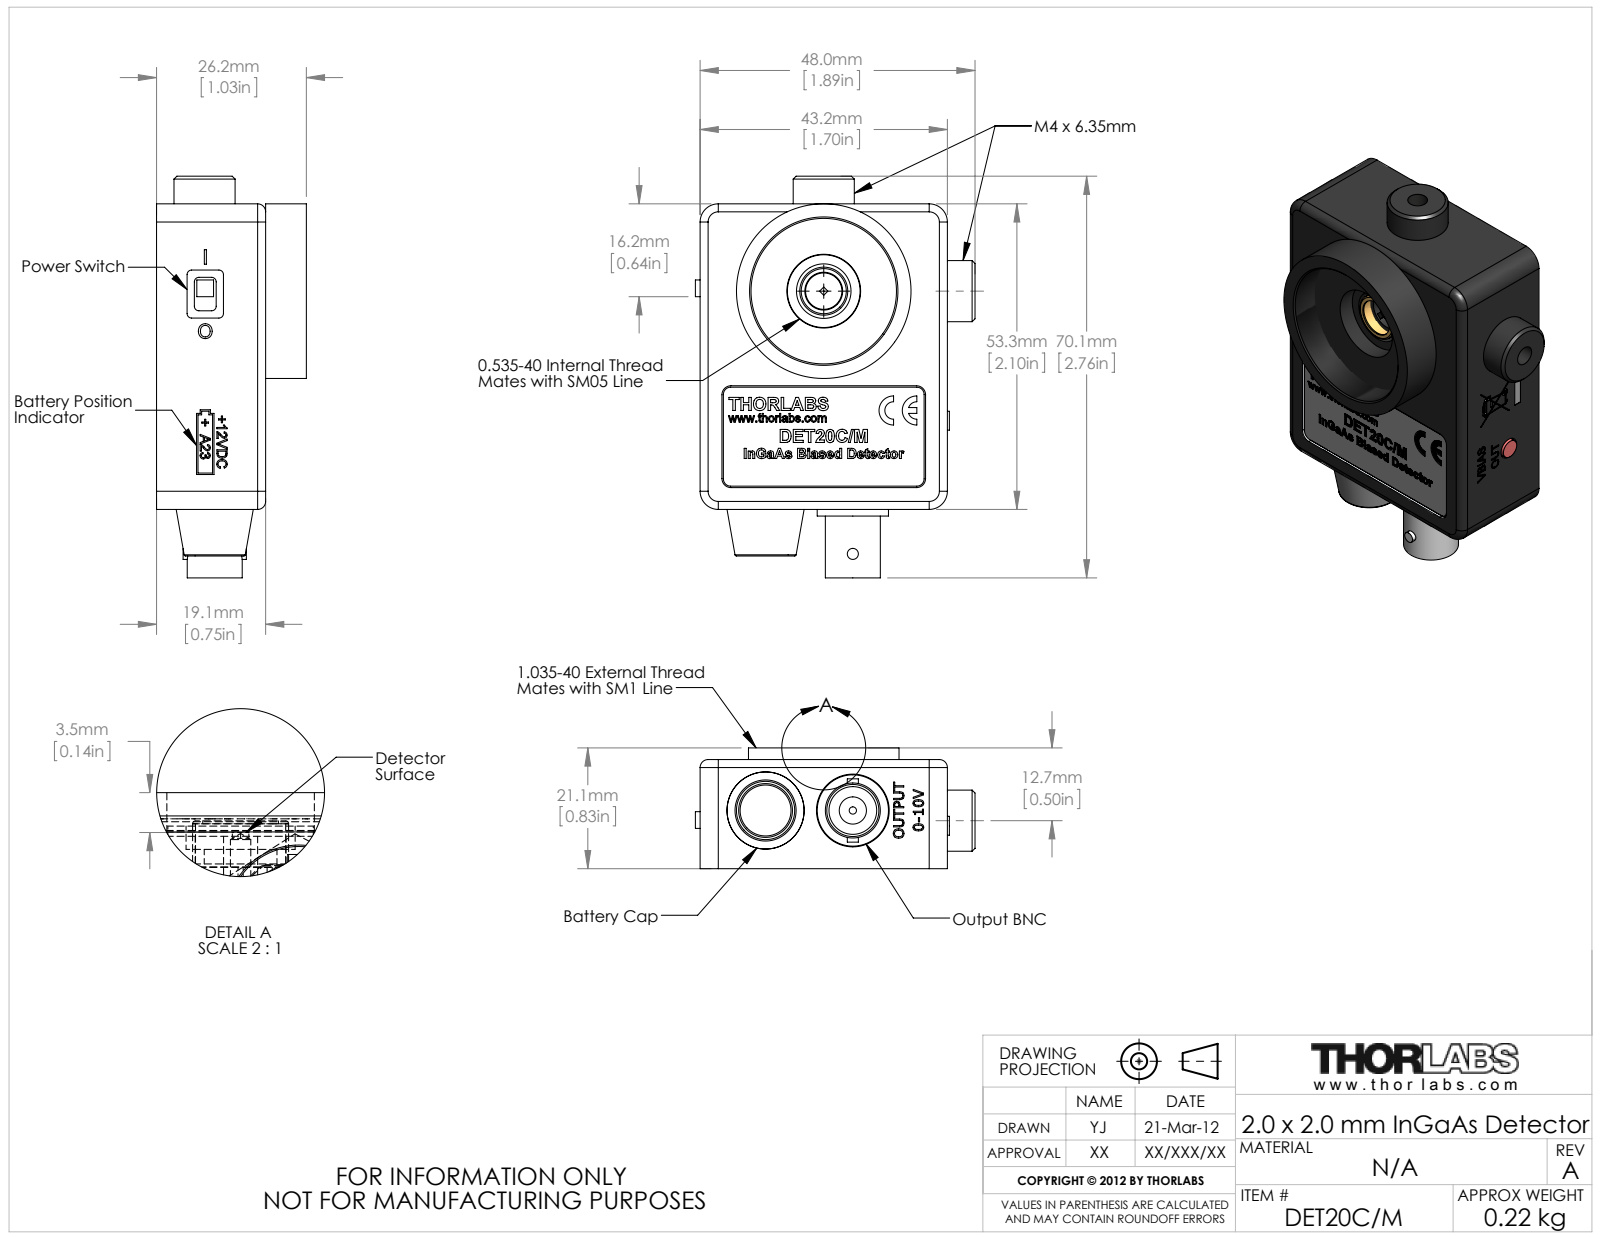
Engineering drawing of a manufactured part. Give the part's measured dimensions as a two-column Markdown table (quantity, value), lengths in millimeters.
| quantity | value |
| --- | --- |
| part name | 23158-E0W |
| STEP written by | SolidWorks 2011 (AUTOMOTIVE_DESIGN) |
| units | millimeters |
| bodies | 14 solids, 1920 faces (1058 planar, 272 cylindrical, 590 other) |
| overall size | 70.12 × 48.83 × 26.16 |
| volume | 22 365 mm³ |
| surface area | 26 273 mm² |
| round holes (diameter × count) | 0.71 × 7, 1.78 × 7, 2.44 × 7, 3.17 × 4, 5.08 × 4, 3.81 × 3, 3.45 × 2, 5.85 × 2, 0.43 × 1, 1.27 × 1, 1.28 × 1, 1.32 × 1 |
| round bosses / shafts (diameter × count) | 1 × 4, 0.45 × 3, 10.67 × 2, 5.99 × 2, 30.48 × 1, 26.29 × 1, 12.7 × 1, 12.45 × 1 |
| partial cylindrical surfaces (radius × count) | 3.17 × 26, 0.79 × 10, 2.41 × 8, 0.1 × 6, 0.5 × 6, 0.4 × 4, 1.27 × 4, 1.4 × 4 |
| main face-to-face distances | 1.59, 11.49, 2.54, 13.08, 1.78, 1.27, 4.19, 0.51, 5.78, 17.27 |
| hole center spacings | 1.27, 2.84, 2.54, 1.8, 3.81, 3.59, 10.24, 17.49 |
